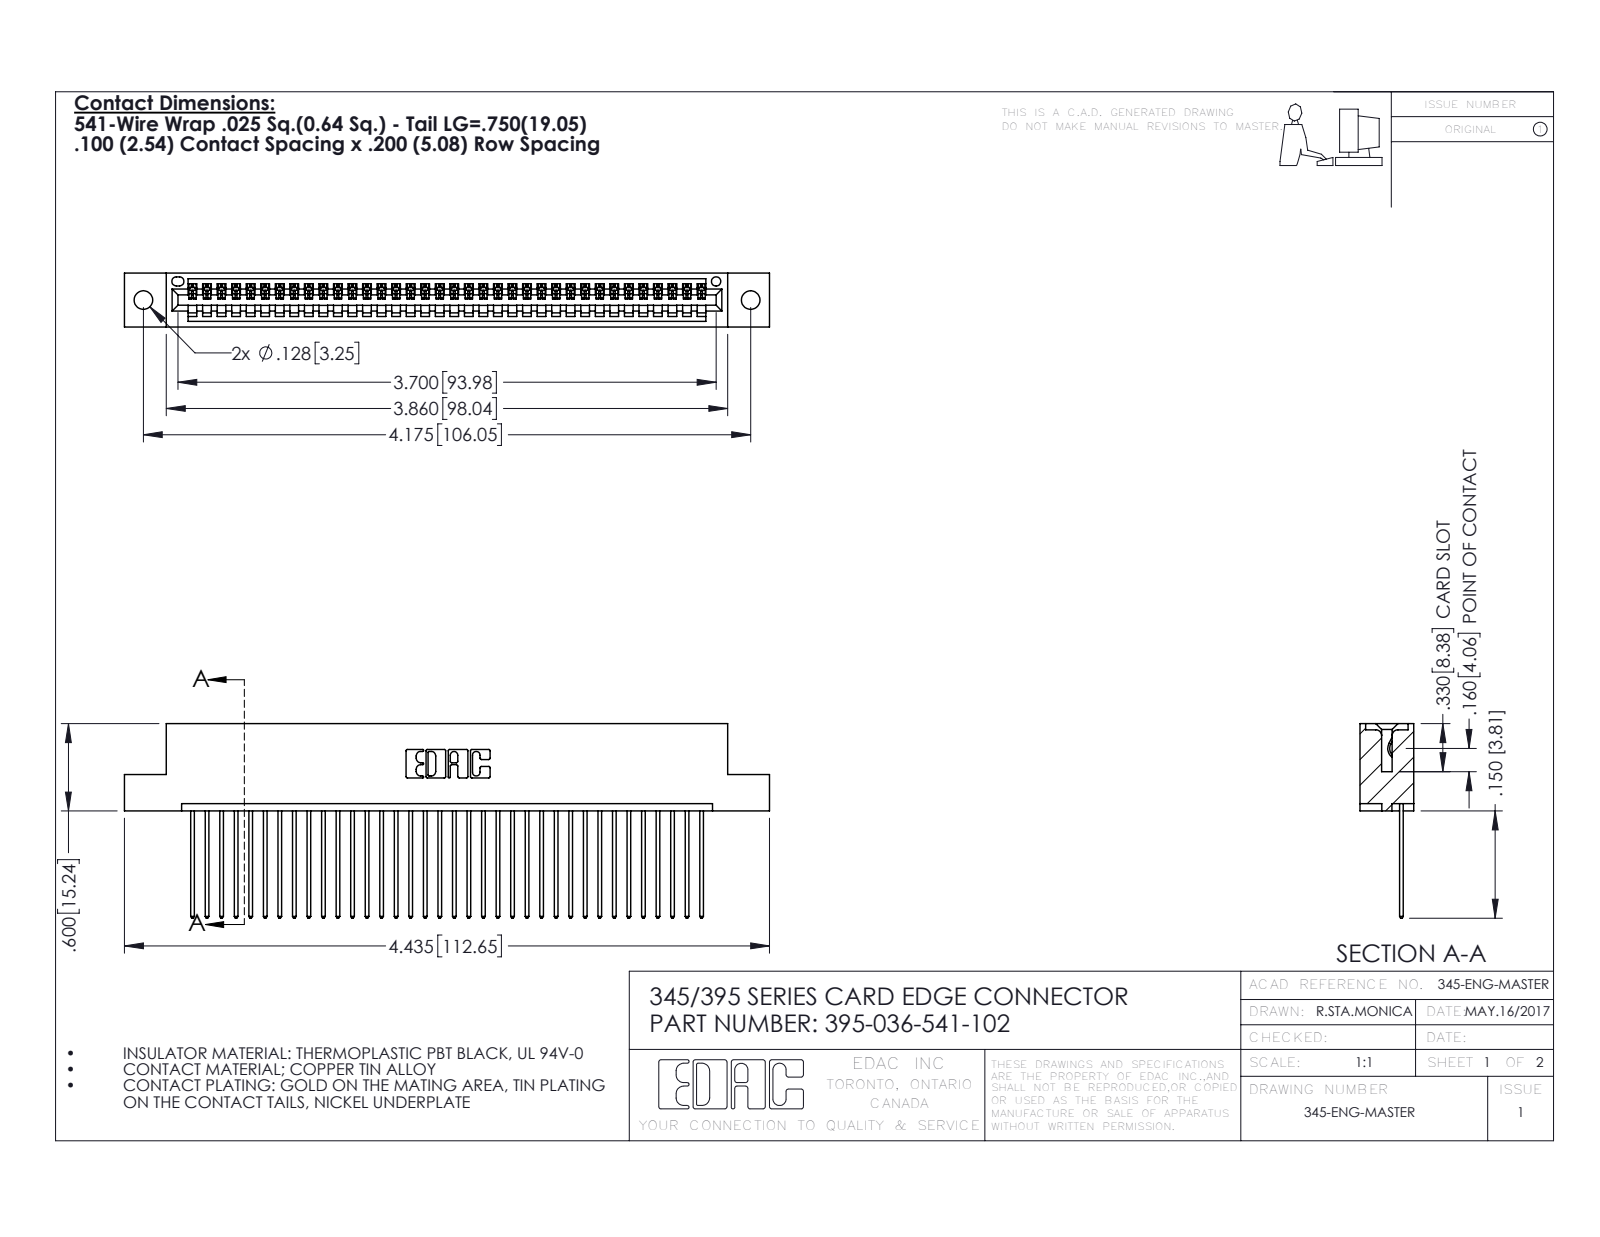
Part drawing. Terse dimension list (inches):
name: 345-292-001_345-293-141; 395-036-541-102; 345 Part_Flush Mounting Lugs - 0.128 Dia
written by: SolidWorks 2016 (CONFIG_CONTROL_DESIGN)
unit: in
bodies: 37 solids, 2214 faces (1520 planar, 694 cylindrical, 0 other)
size: 4.435 × 1.337 × 0.37
volume: 0.655 in³; area: 22.64 in²
holes: 2× ⌀0.128, 1× ⌀0.064
rounds: 72× R0.006, 72× R0.01, 22× R0.01, 6× R0.007, 6× R0.031, 3× R0.026, 2× R0.031, 2× R0.04
face distances: 0.072, 0.298, 0.098, 0.272, 0.025, 0.37, 0.2, 0.225, 0.149, 0.072
hole spacings: 0.27, 3.939, 4.175
